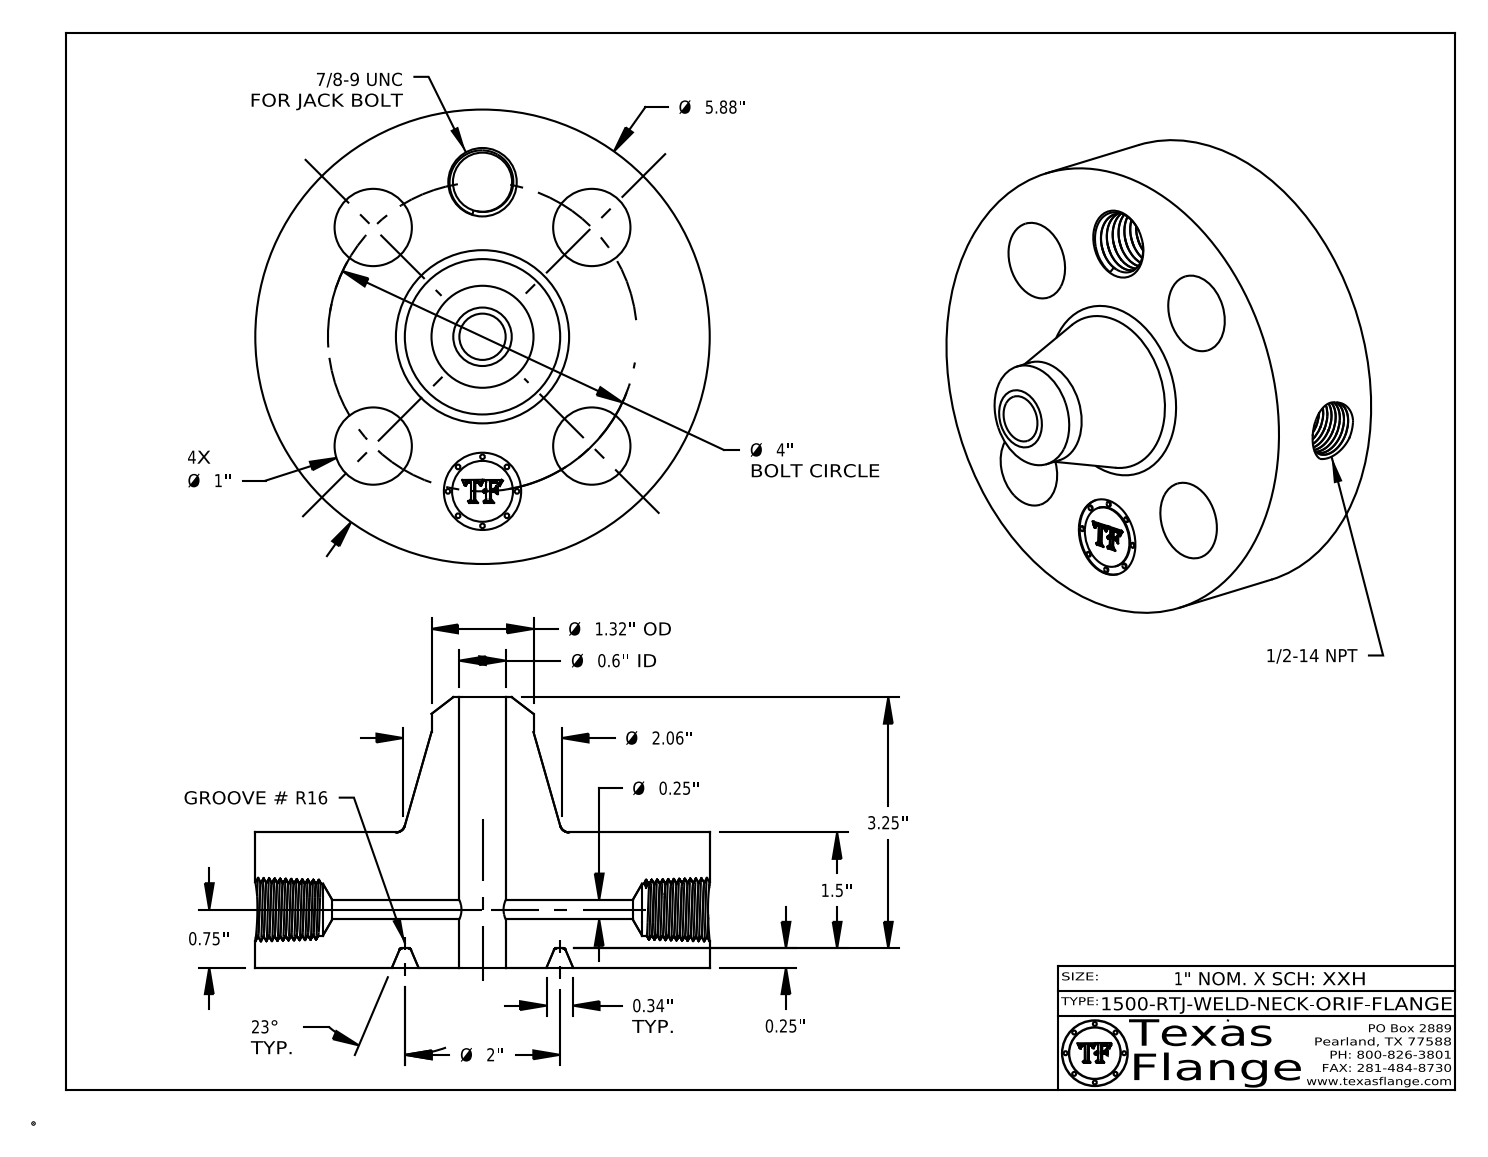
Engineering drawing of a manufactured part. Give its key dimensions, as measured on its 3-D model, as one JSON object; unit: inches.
{"part_name": "1500-RTJ-WELD-NECK", "step_written_by": "CATIA V5 STEP AP214 (AUTOMOTIVE_DESIGN)", "units": "inches", "bodies": {"solids": 1, "faces": 771, "planar": 370, "cylindrical": 85, "other": 316}, "overall_size": [5.88, 5.88, 3.5], "volume_in3": 42.27, "surface_area_in2": 131.4, "round_holes": [[1, 5], [0.25, 1], [0.599, 1], [0.672, 1], [0.766, 1]], "round_bosses_or_shafts": [[0.061, 8], [5.88, 1], [1.32, 1], [0.788, 1]], "face_to_face_distances": [1.75, 0.25, 1.5, 1.735, 1.485, 0.015, 3.5, 3.25, 1.765, 0.298], "hole_center_spacings": [2, 1.531, 2.828, 3.695, 4]}
